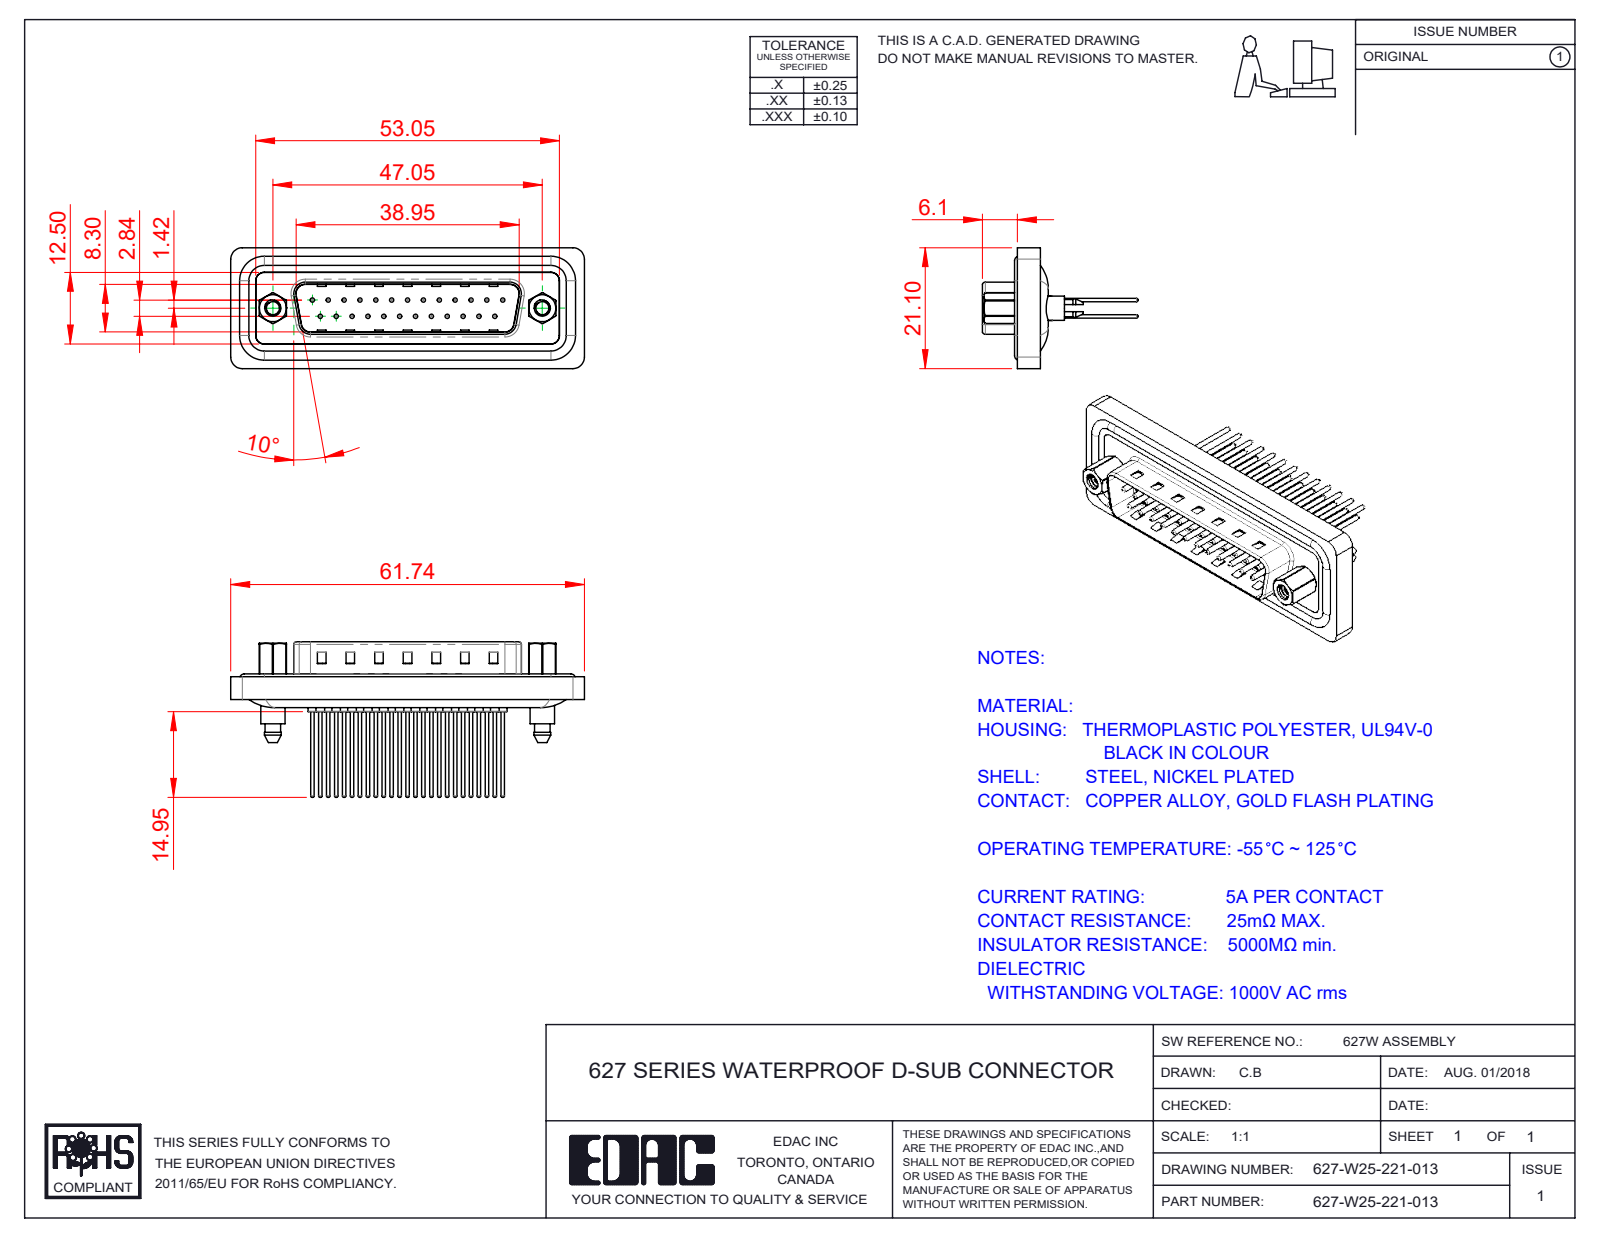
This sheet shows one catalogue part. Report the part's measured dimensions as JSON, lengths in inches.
{"part_name": "627W 4-40 Hex Standoff; 627W Waterproof Housing_25 Contacts BL; 627W Contact Row 1_21; 627-W25-221-013 (+4 more)", "step_written_by": "SolidWorks 2020 (CONFIG_CONTROL_DESIGN)", "units": "inches", "bodies": {"solids": 33, "faces": 1541, "planar": 394, "cylindrical": 648, "other": 499}, "overall_size": [2.431, 1.069, 0.831], "volume_in3": 0.393, "surface_area_in2": 17.59, "round_holes": [[0.03, 25], [0.059, 25], [0.063, 25], [0.079, 25], [0.089, 2], [0.09, 2], [0.157, 2], [0.167, 2], [0.189, 2]], "round_bosses_or_shafts": [[0.024, 25], [0.059, 8], [0.063, 4], [0.213, 2], [0.193, 2], [0.11, 2], [0.167, 1]], "partial_cylinders_radius": [[0.059, 14], [0.079, 12], [0.02, 8], [0.063, 6], [0.035, 4], [0.106, 4], [0.169, 4], [0.016, 2]], "face_to_face_distances": [0.016, 0.063, 0.098, 0.043, 0.114, 0.222, 0.161, 0.177, 0.608, 0.03], "hole_center_spacings": [0.124, 0.218, 0.109, 0.436, 0.198, 0.327, 0.545, 0.198]}
